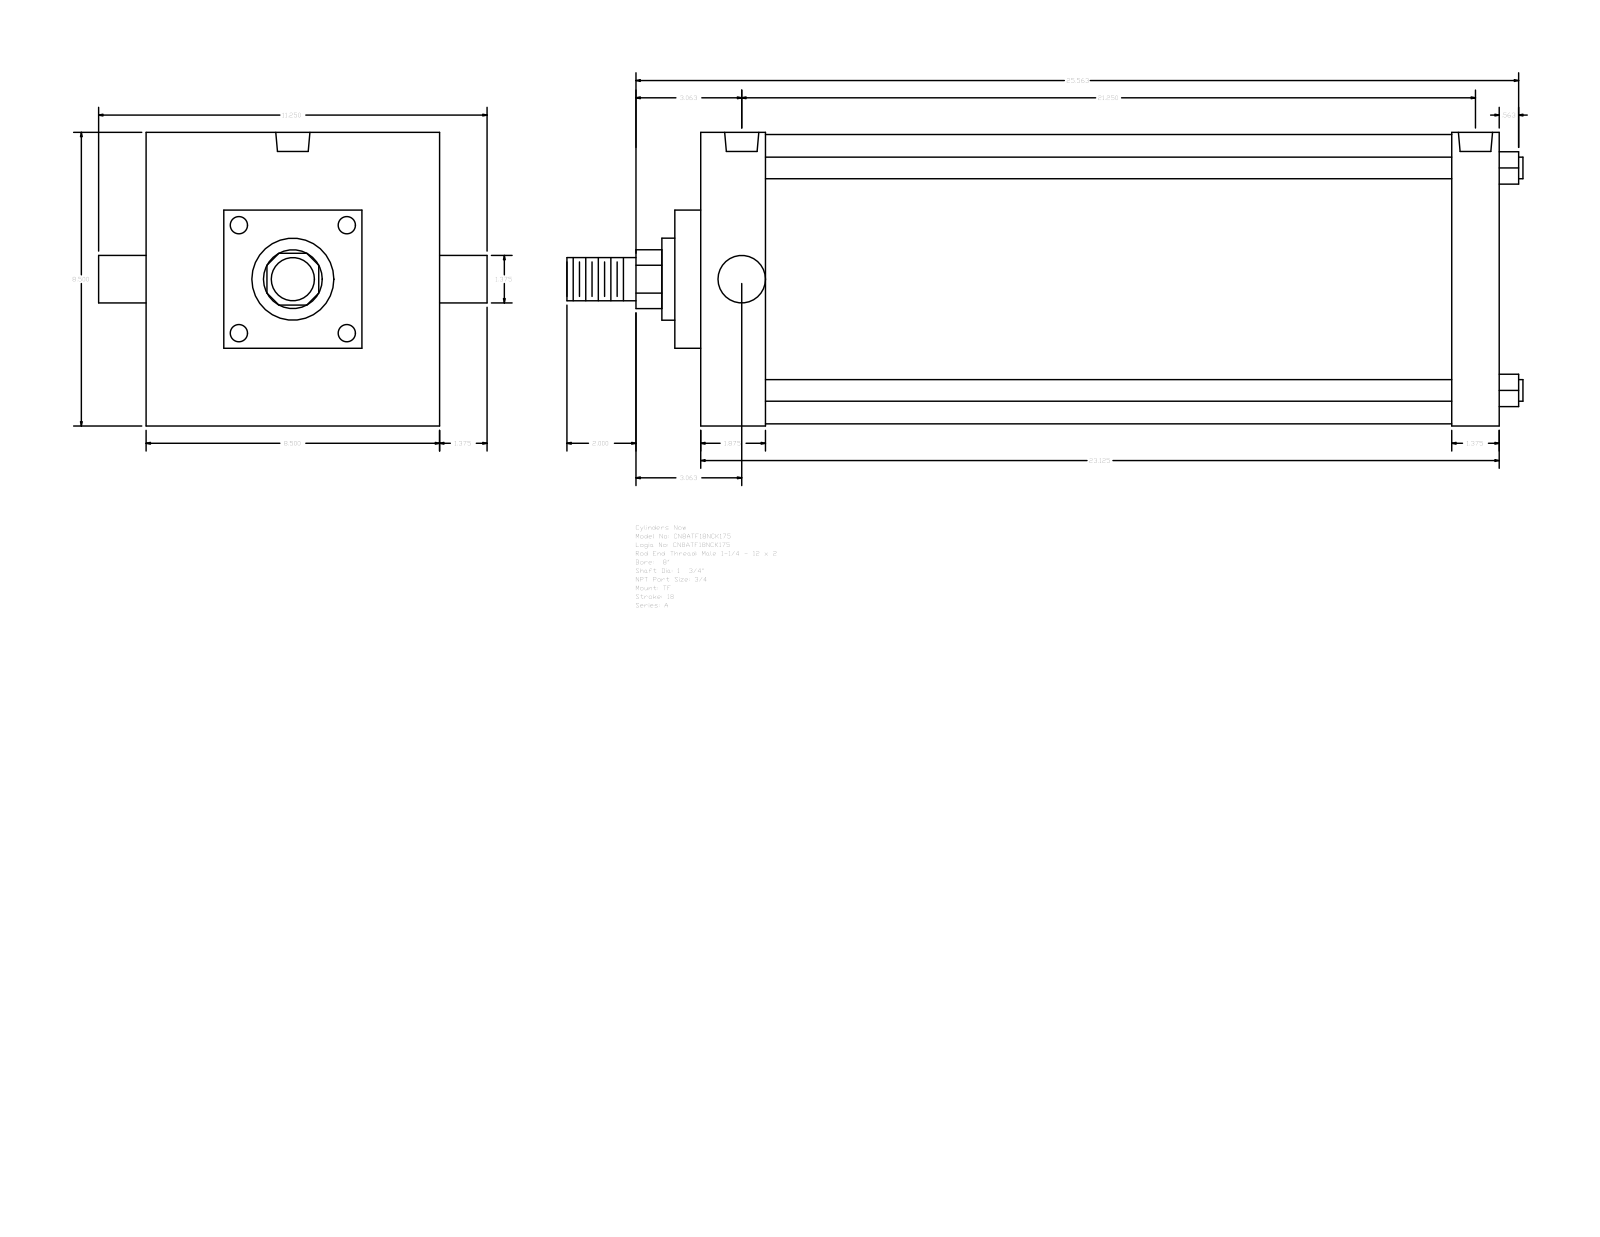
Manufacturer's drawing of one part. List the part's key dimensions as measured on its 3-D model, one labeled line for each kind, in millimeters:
Part name (STEP PRODUCT): A_TF__0800_1.75
STEP written by: GSSL Pune (CONFIG_CONTROL_DESIGN)
Units: millimetres
Bodies: 0 solids, 89 faces (65 planar, 24 cylindrical, 0 other)
Overall size (bounding box): 703.26 × 285.75 × 215.9
Round holes (diameter × count): ⌀15.08 ×3, ⌀25.12 ×2
Round bosses / shafts (diameter × count): ⌀15.88 ×4, ⌀212.72 ×1, ⌀60.33 ×1, ⌀44.45 ×1, ⌀34.92 ×1, ⌀31.75 ×1
Partial cylindrical surfaces — rounded edges, fillets, slot ends (radius × count): R21.63 ×1
Main face-to-face distances: 587.38, 215.9, 47.63, 539.75, 552.46, 504.83, 34.92, 19.05, 57.15, 158.75
Hole centre spacings: 6.35, 533.4, 527.05, 539.75
